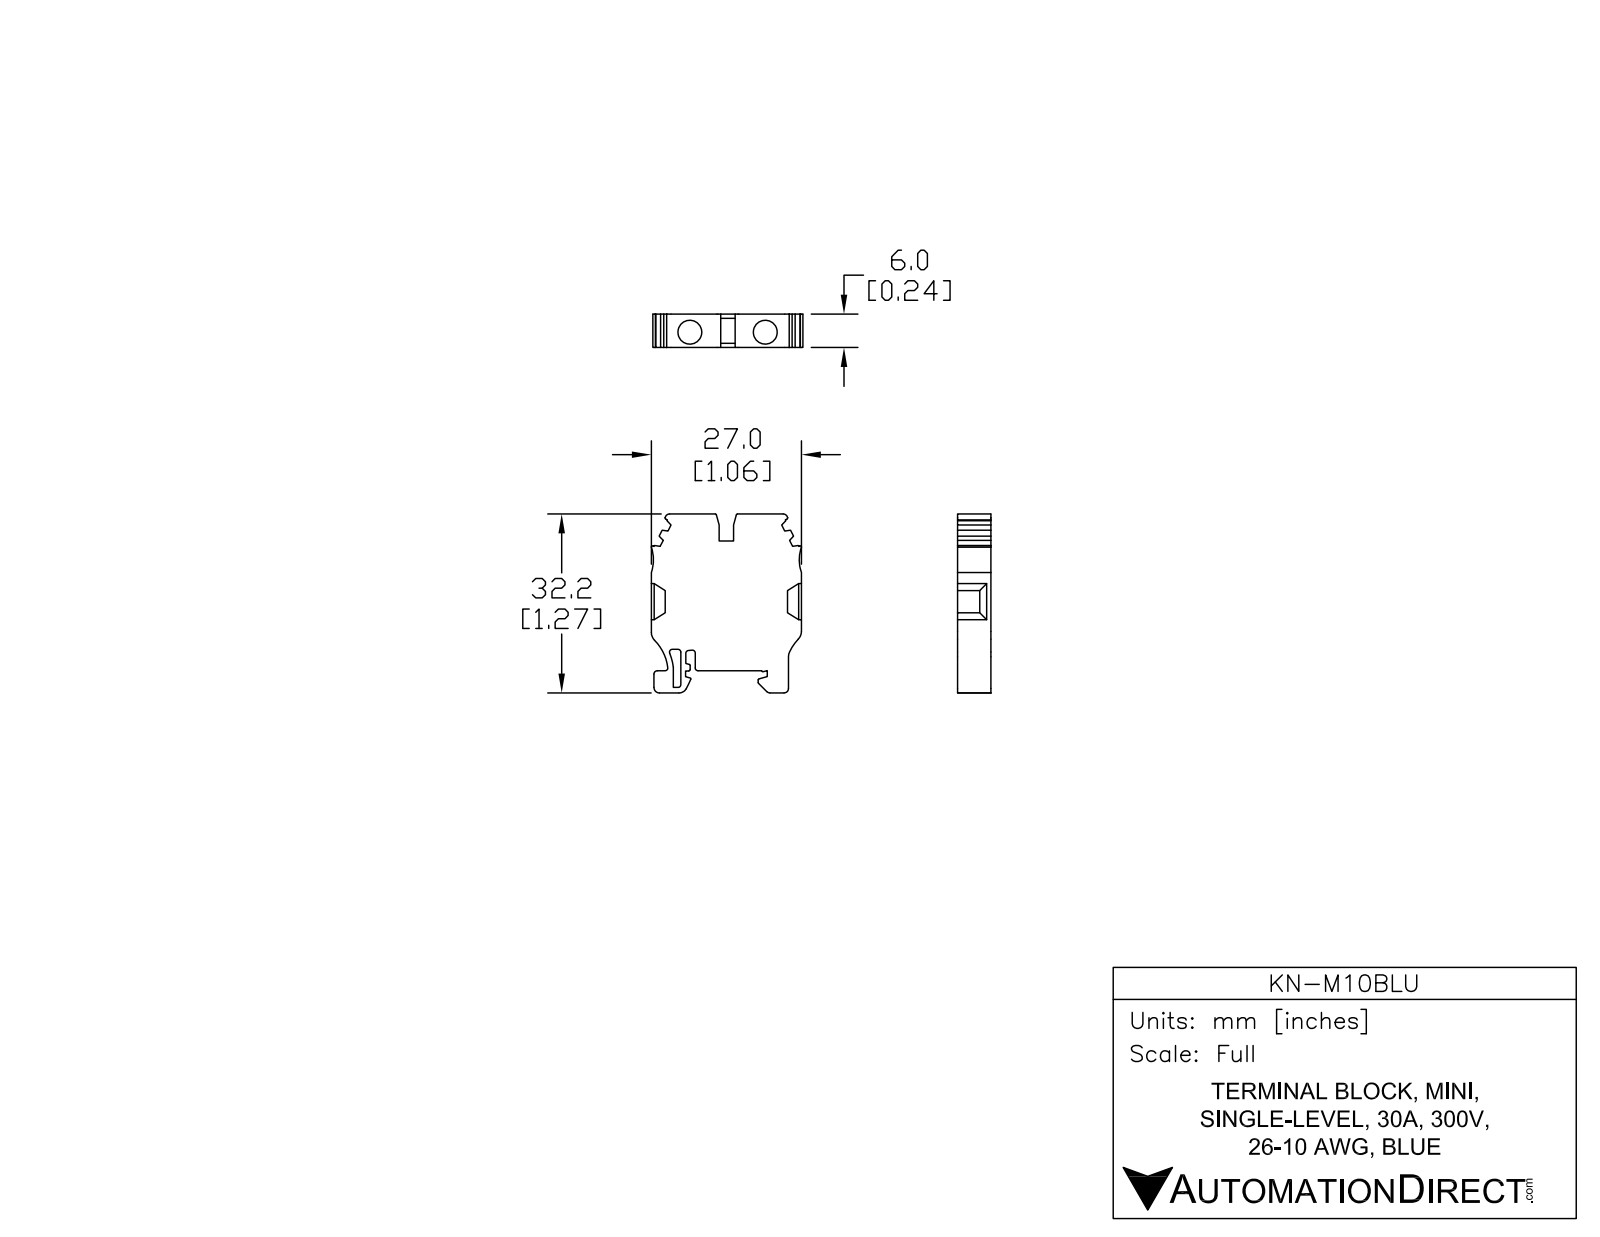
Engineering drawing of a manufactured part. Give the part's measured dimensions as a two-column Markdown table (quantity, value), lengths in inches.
| quantity | value |
| --- | --- |
| part name | KN-M10 |
| STEP written by | SolidWorks 2014 (AUTOMOTIVE_DESIGN) |
| units | inches |
| bodies | 1 solid, 126 faces (84 planar, 42 cylindrical, 0 other) |
| overall size | 1.268 × 1.063 × 0.236 |
| volume | 0.248 in³ |
| surface area | 3.979 in² |
| round holes (diameter × count) | 0.169 × 2 |
| partial cylindrical surfaces (radius × count) | 0.008 × 11, 0.02 × 7, 0.031 × 4, 0.079 × 3, 0.273 × 2, 0.012 × 1, 0.024 × 1, 0.039 × 1 |
| main face-to-face distances | 0.236, 1.111, 0.48, 0.583, 0.098, 0.763, 0.118, 0.965, 0.382, 0.484 |
| hole center spacings | 0.535 |
